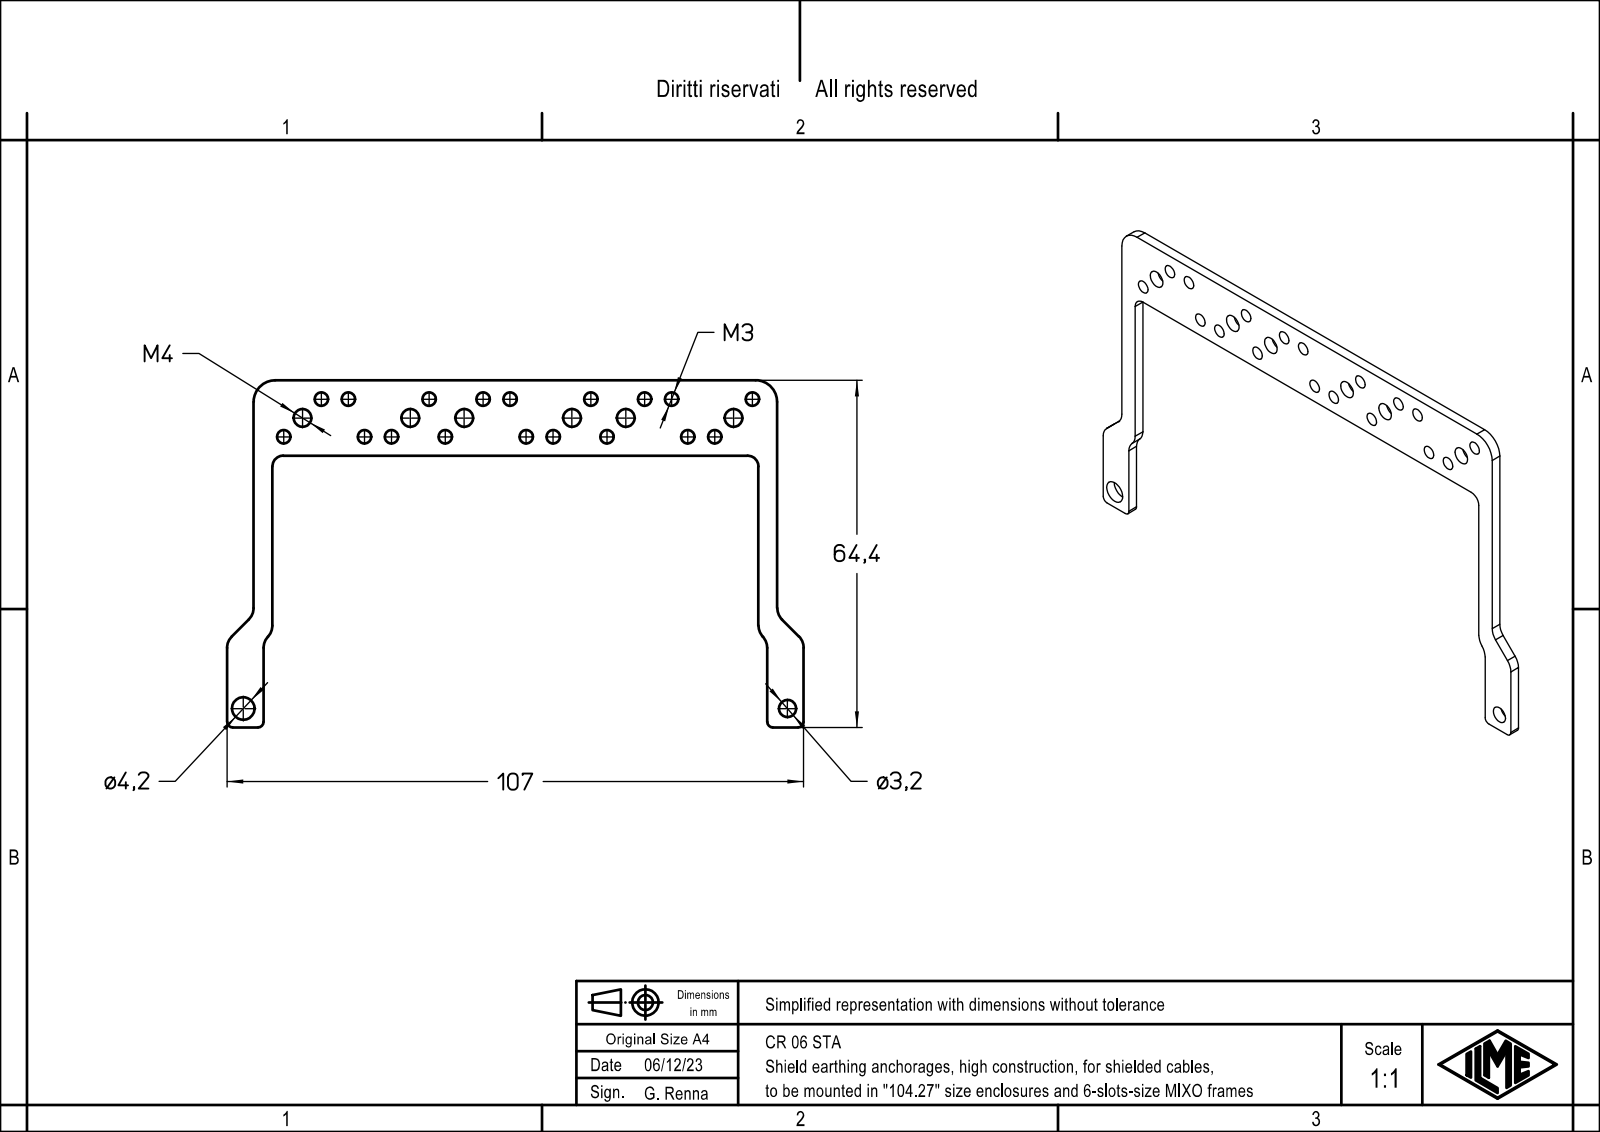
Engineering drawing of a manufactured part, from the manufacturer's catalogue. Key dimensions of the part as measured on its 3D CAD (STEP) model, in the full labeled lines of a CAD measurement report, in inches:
Part name (STEP PRODUCT): CR_24_STA
STEP written by: Creo Elements/Direct Modeling 20.5B 27-May-2023 (C) Parametric Technology GmbH (AUTOMOTIVE_DESIGN)
Units: inches
Bodies: 1 solid, 84 faces (16 planar, 68 cylindrical, 0 other)
Overall size (bounding box): 4.213 × 2.535 × 0.079
Volume: 0.204 in³ · Surface area: 7.211 in²
Round holes (diameter × count): ⌀0.098 ×18, ⌀0.13 ×6, ⌀0.126 ×1, ⌀0.165 ×1
Partial cylindrical surfaces — rounded edges, fillets, slot ends (radius × count): R0.118 ×8, R0.039 ×4, R0.079 ×2, R0.157 ×2
Main face-to-face distances: 0.079, 0.551, 0.138, 3.689, 3.827, 3.551, 0.193, 0.331, 3.882, 3.947
Hole centre spacings: 1.181, 0.195, 0.591, 0.787, 1.052, 1.326, 2.362, 0.197
